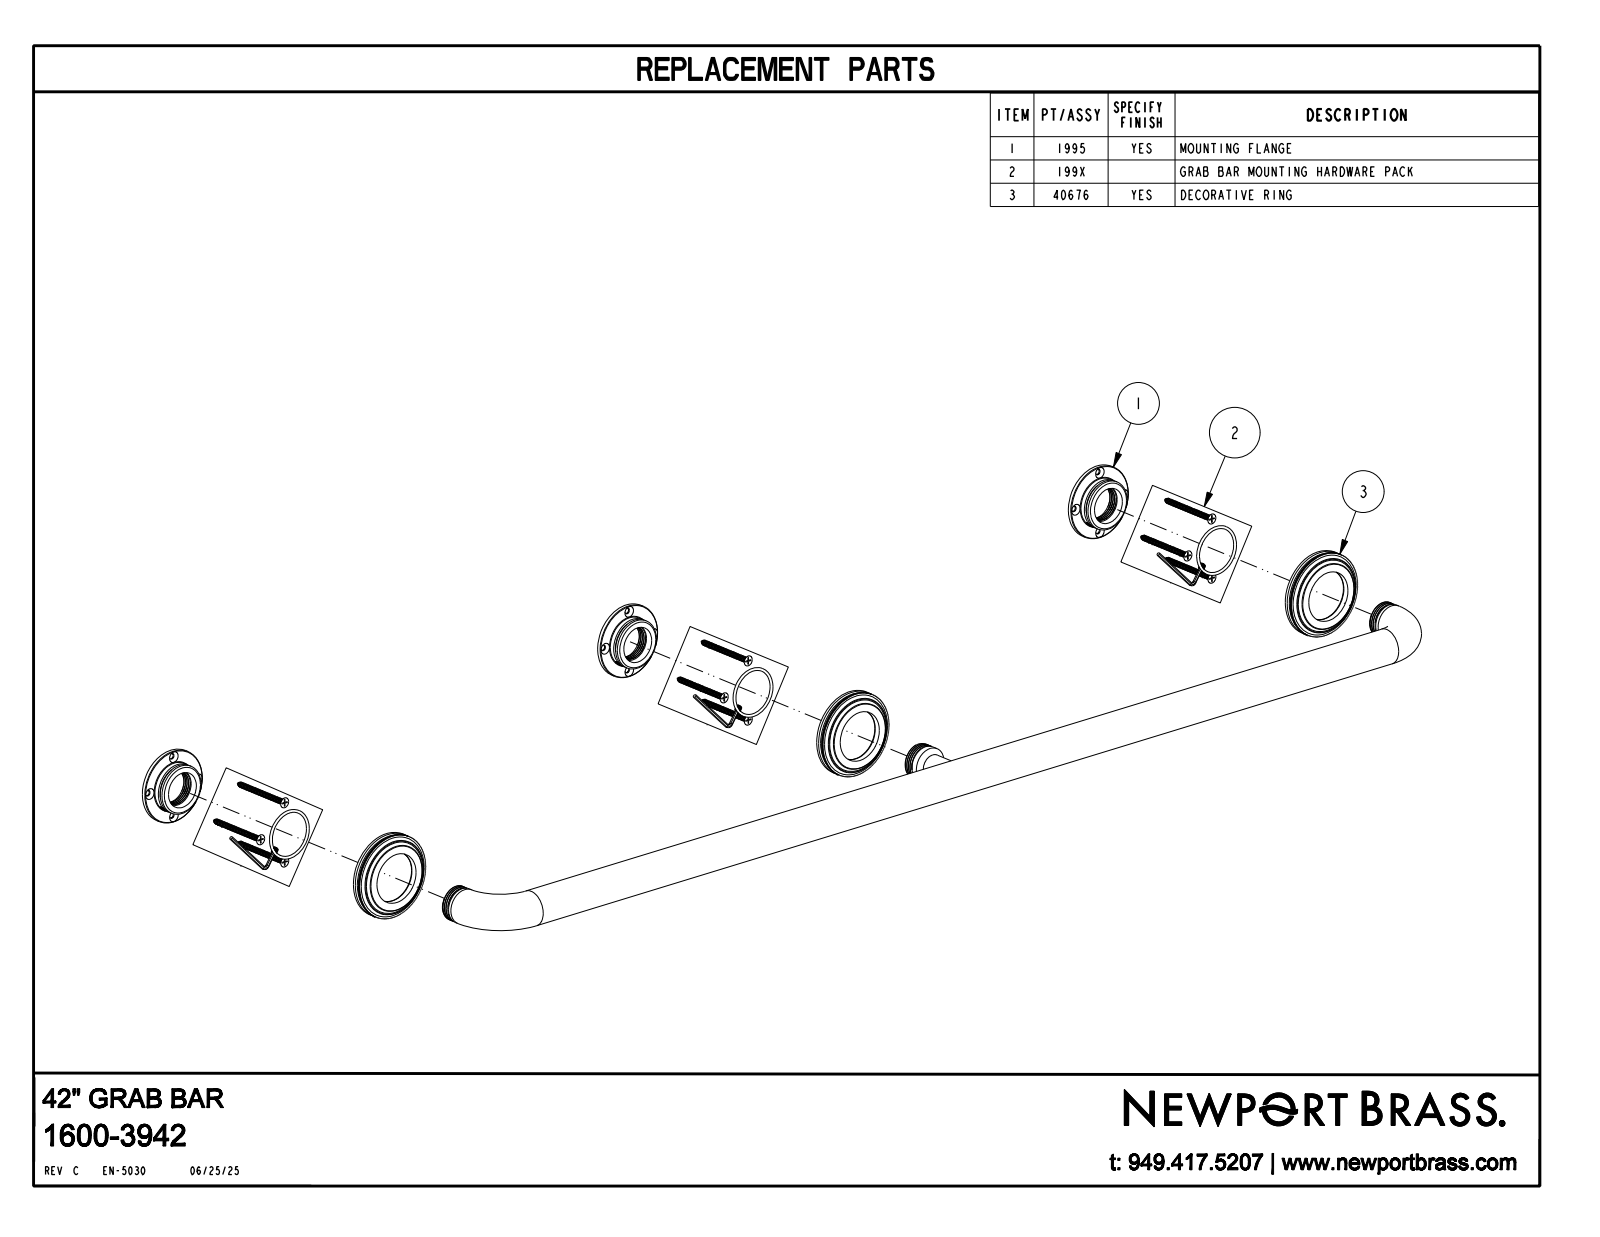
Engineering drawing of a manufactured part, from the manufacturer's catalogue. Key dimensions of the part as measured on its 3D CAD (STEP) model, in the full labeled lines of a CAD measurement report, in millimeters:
Part name (STEP PRODUCT): 1600-3942
STEP written by: CREO PARAMETRIC BY PTC INC, 2018400 (CONFIG_CONTROL_DESIGN)
Units: millimetres
Bodies: 1 solid, 1707 faces (1099 planar, 563 cylindrical, 45 other)
Overall size (bounding box): 1143 × 76.2 × 69.9
Volume: 1 056 000 mm³ · Surface area: 146 500 mm²
Round bosses / shafts (diameter × count): ⌀76.2 ×3, ⌀73.7 ×3, ⌀44.5 ×3, ⌀31.8 ×1, ⌀21.6 ×1
Partial cylindrical surfaces — rounded edges, fillets, slot ends (radius × count): R15.9 ×1
Main face-to-face distances: 13.3, 15.2, 1.9, 8.3, 5.1, 7, 2.5, 6.4, 1.9, 7
